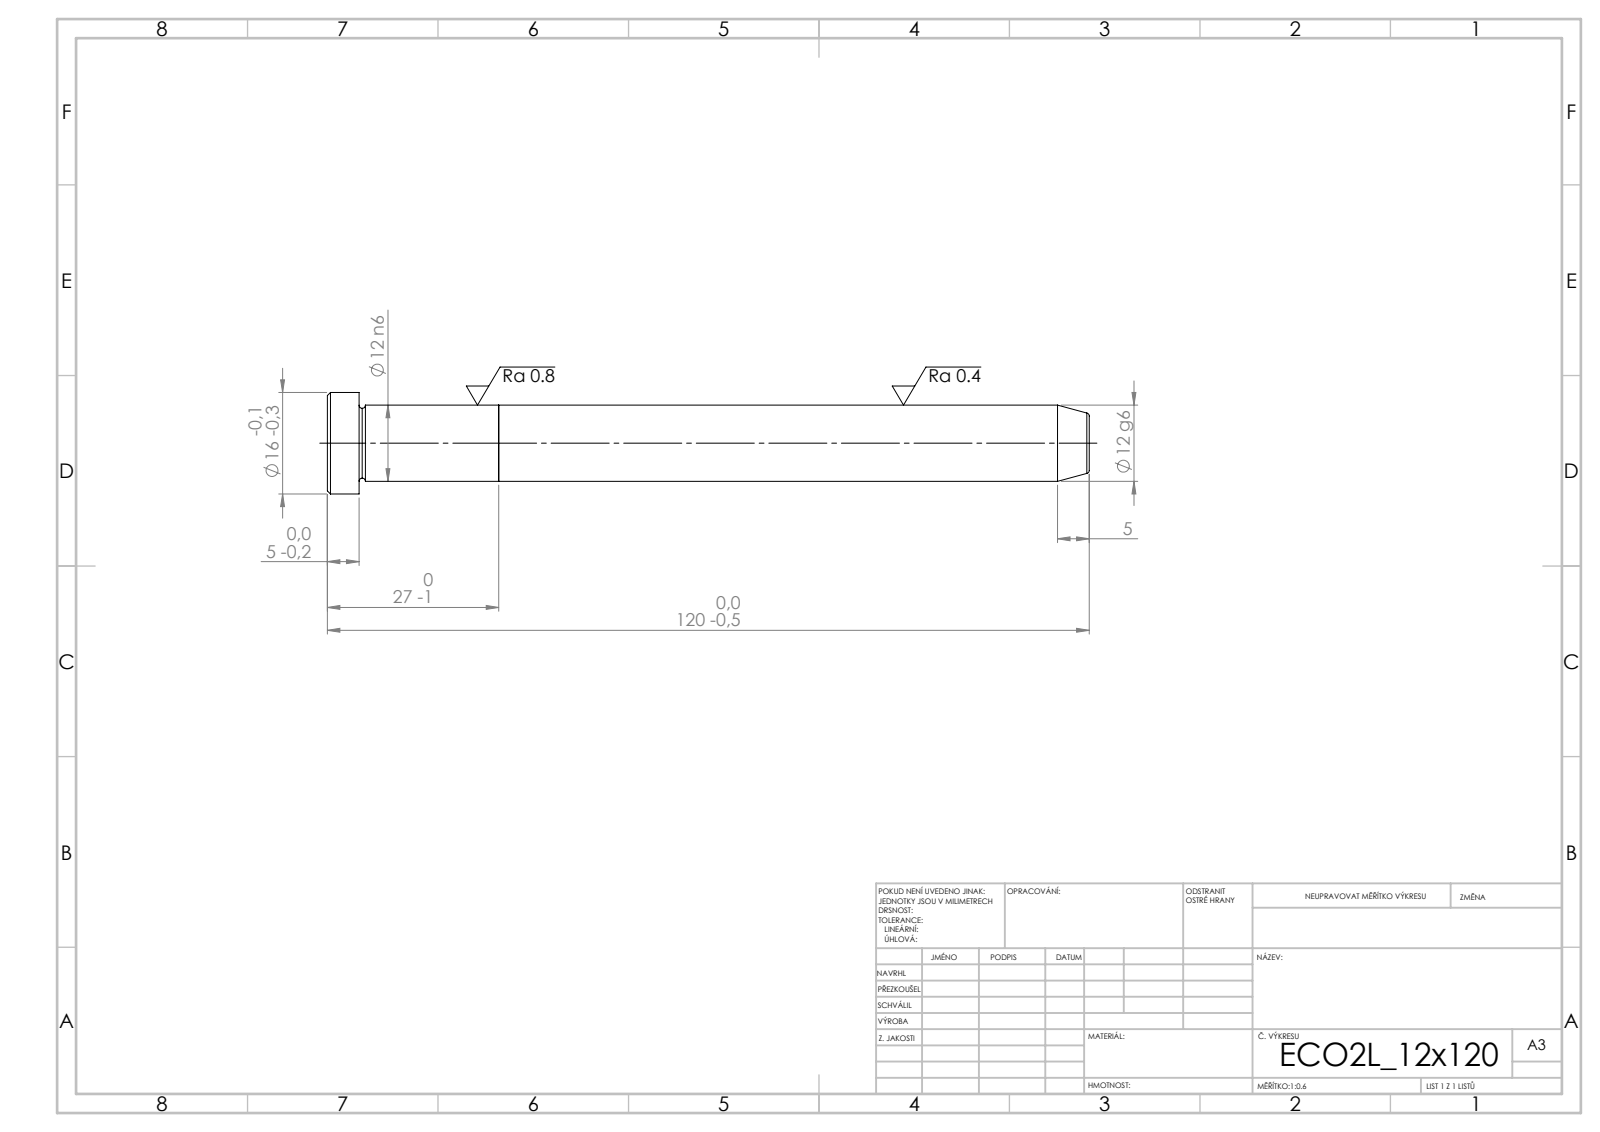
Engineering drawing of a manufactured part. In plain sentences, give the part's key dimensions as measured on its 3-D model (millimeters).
Its 3-D file was written by "SolidWorks 2019 (CONFIG_CONTROL_DESIGN)". It is 2 solids with 21 faces: 5 planar, 6 cylindrical and 10 other. Overall it measures 120 by 16 by 16 millimeters. Its volume is 13 873 cubic millimeters and its surface area 5 155 square millimeters. Round bosses or shafts: 1 of diameter 16, 1 of diameter 12. The main face-to-face distances are 27, 22, 5, 93, 115, 120.
